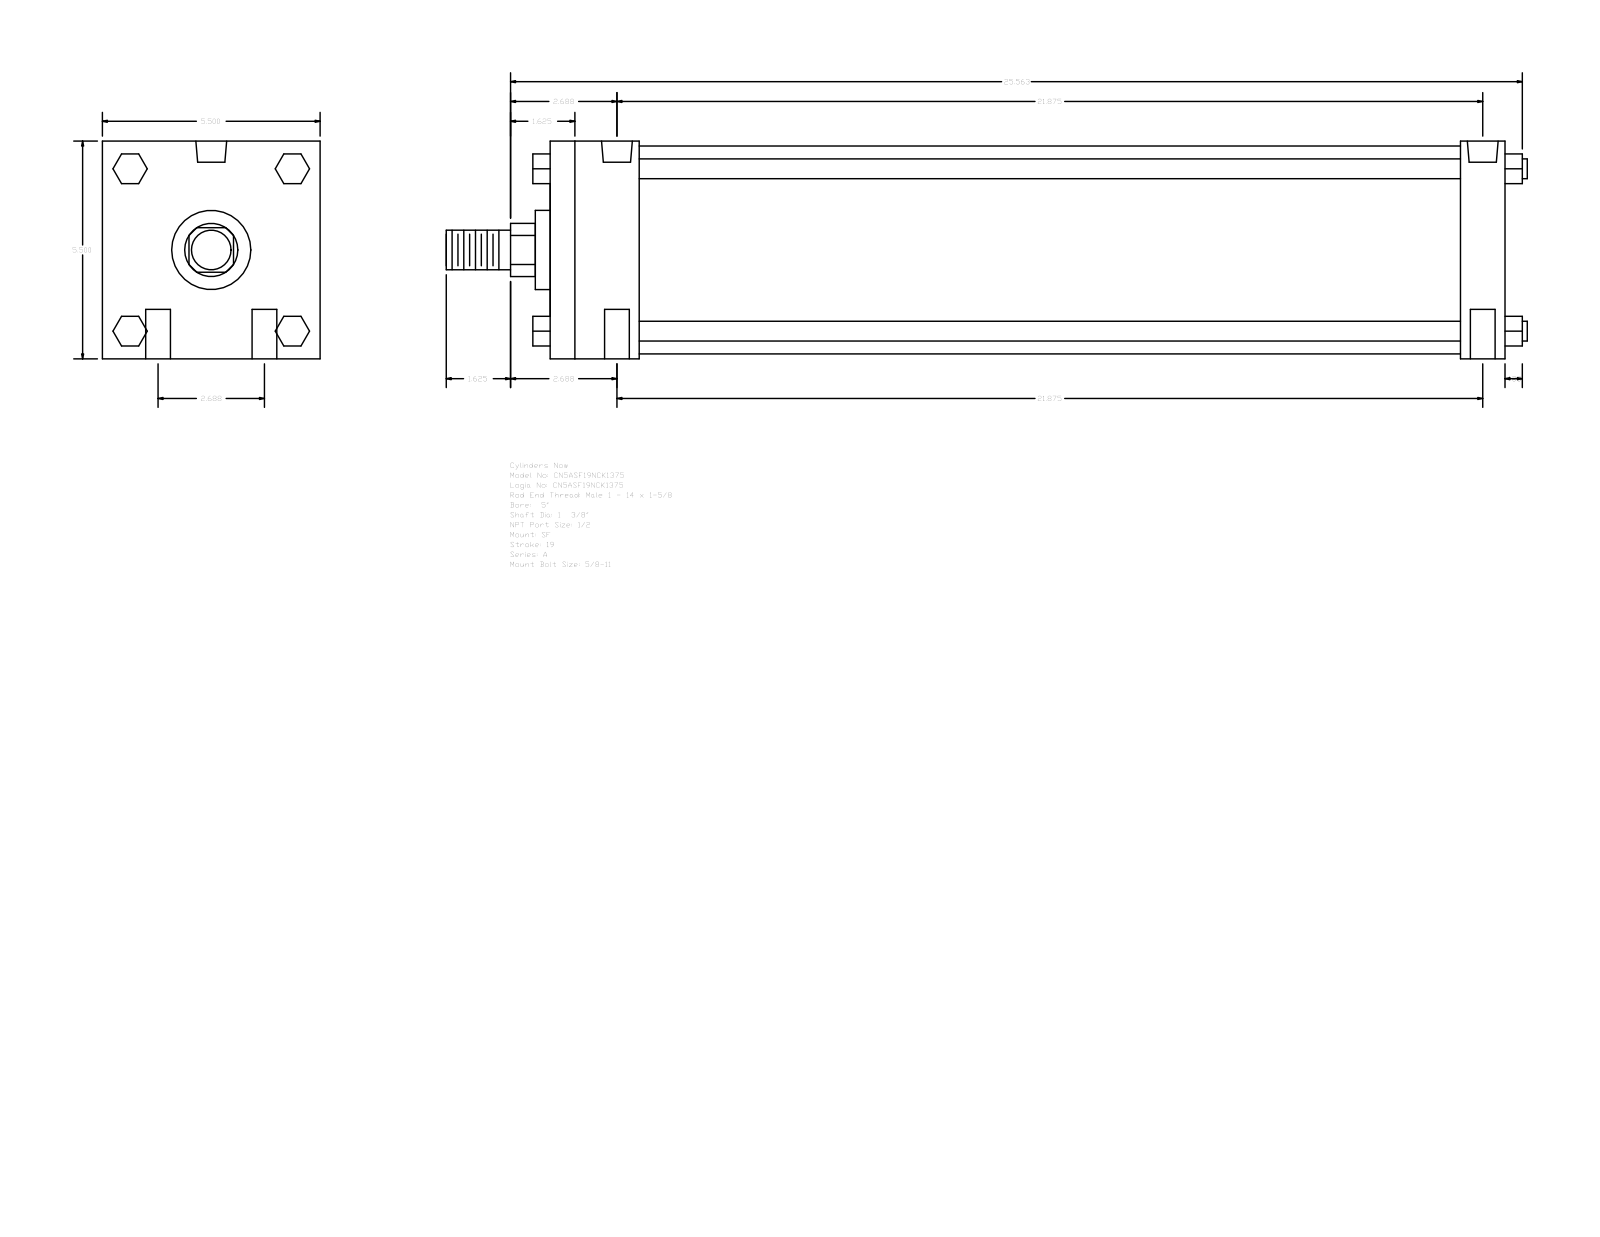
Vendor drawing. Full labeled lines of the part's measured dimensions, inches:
Part name (STEP PRODUCT): A_SF__0500_1.375
STEP written by: GSSL Pune (CONFIG_CONTROL_DESIGN)
Units: inches
Bodies: 0 solids, 124 faces (94 planar, 30 cylindrical, 0 other)
Overall size (bounding box): 27.313 × 5.5 × 5.5
Round holes (diameter × count): ⌀0.625 ×4, ⌀0.344 ×2, ⌀0.778 ×2
Round bosses / shafts (diameter × count): ⌀0.5 ×4, ⌀5.25 ×1, ⌀2 ×1, ⌀1.375 ×1, ⌀1 ×1
Partial cylindrical surfaces — rounded edges, fillets, slot ends (radius × count): R0.672 ×1
Main face-to-face distances: 5.5, 24.125, 2.25, 23, 20.75, 21.875, 1.125, 0.75, 2.05, 3.55
Hole centre spacings: 1.344, 21.917, 21.875, 2.687, 22.04, 21.687
